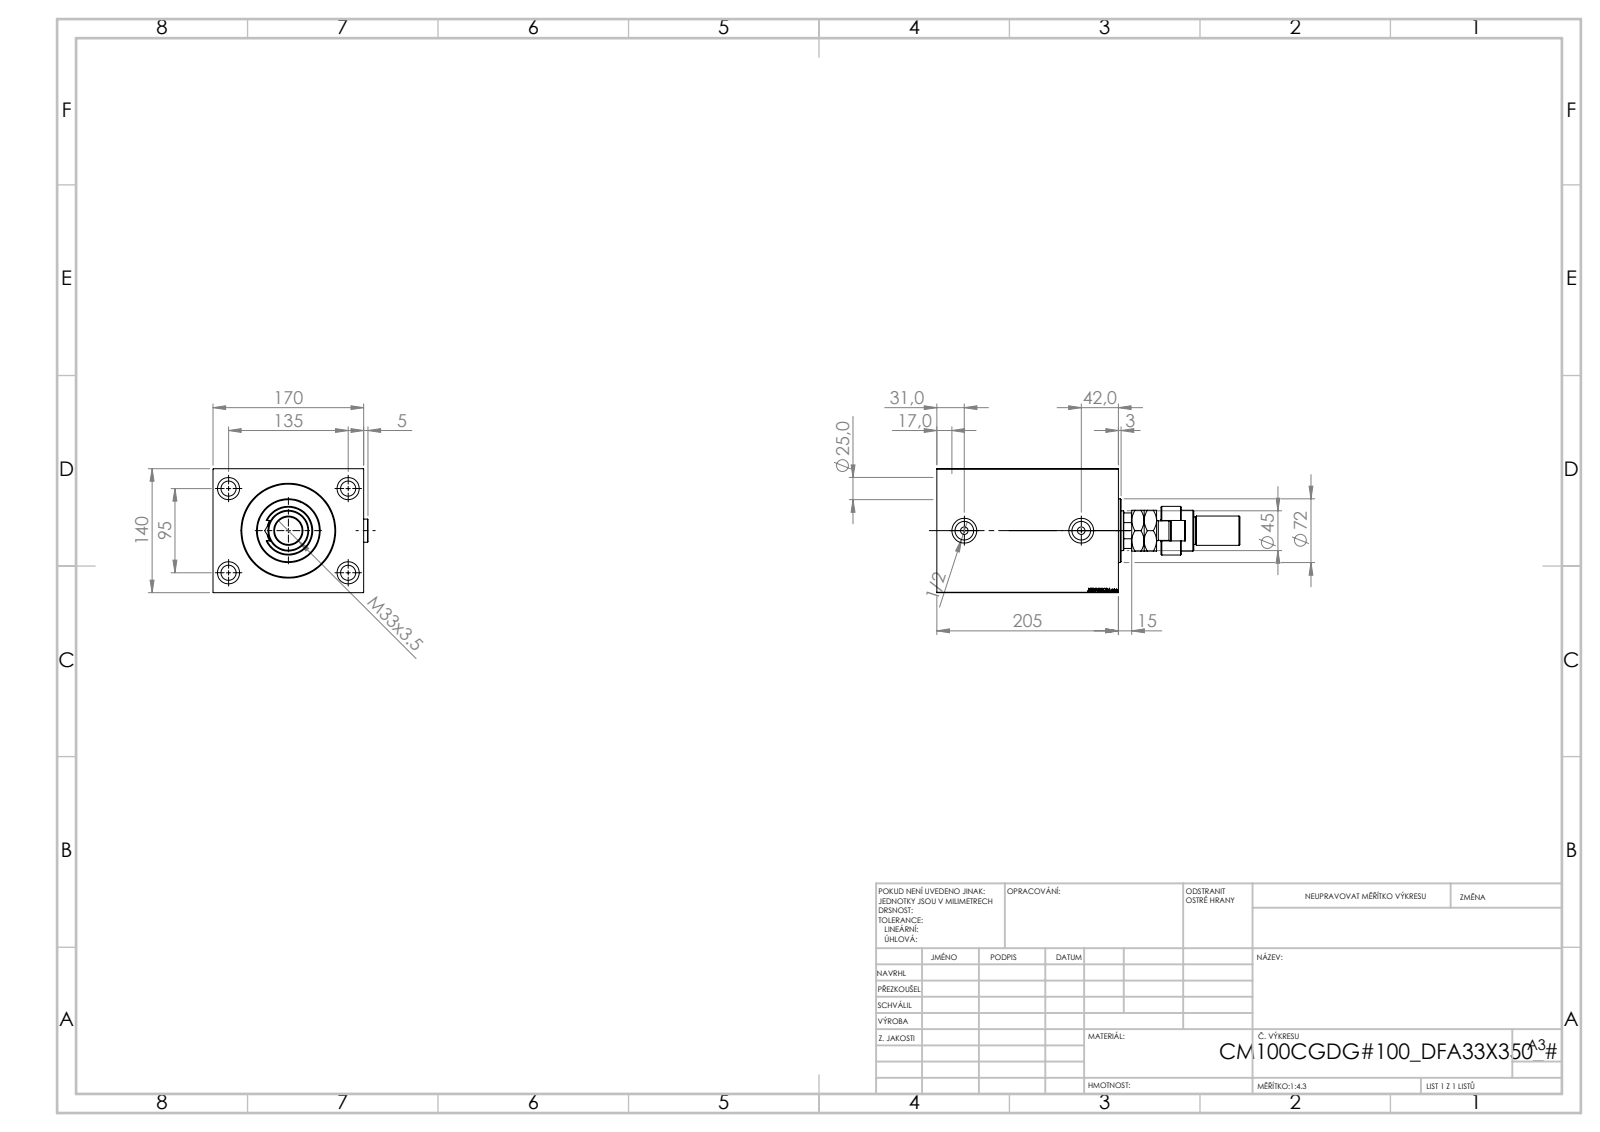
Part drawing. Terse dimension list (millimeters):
name: V450CM_C_Body; V450CM_VC_B; V450CM_C_VCP; MFA (+2 more)
written by: SolidWorks 2019 (CONFIG_CONTROL_DESIGN)
unit: mm
bodies: 7 solids, 1004 faces (471 planar, 91 cylindrical, 442 other)
size: 342 × 174.9 × 140
volume: 4 172 000 mm³; area: 395 421 mm²
holes: 4× ⌀17, 4× ⌀25, 2× ⌀8.5, 2× ⌀20.96, 2× ⌀28, 1× ⌀31.5, 1× ⌀39, 1× ⌀45, 1× ⌀48.5, 1× ⌀100, 1× ⌀102, 1× ⌀105
bosses: 2× ⌀26, 1× ⌀72, 1× ⌀55, 1× ⌀46, 1× ⌀35, 1× ⌀33, 1× ⌀31, 1× ⌀22
rounds: 1× R11.5, 1× R22
face distances: 140, 170, 205, 26, 179, 15, 90, 190, 64, 100
hole spacings: 82.54, 95, 135, 165.08, 132
